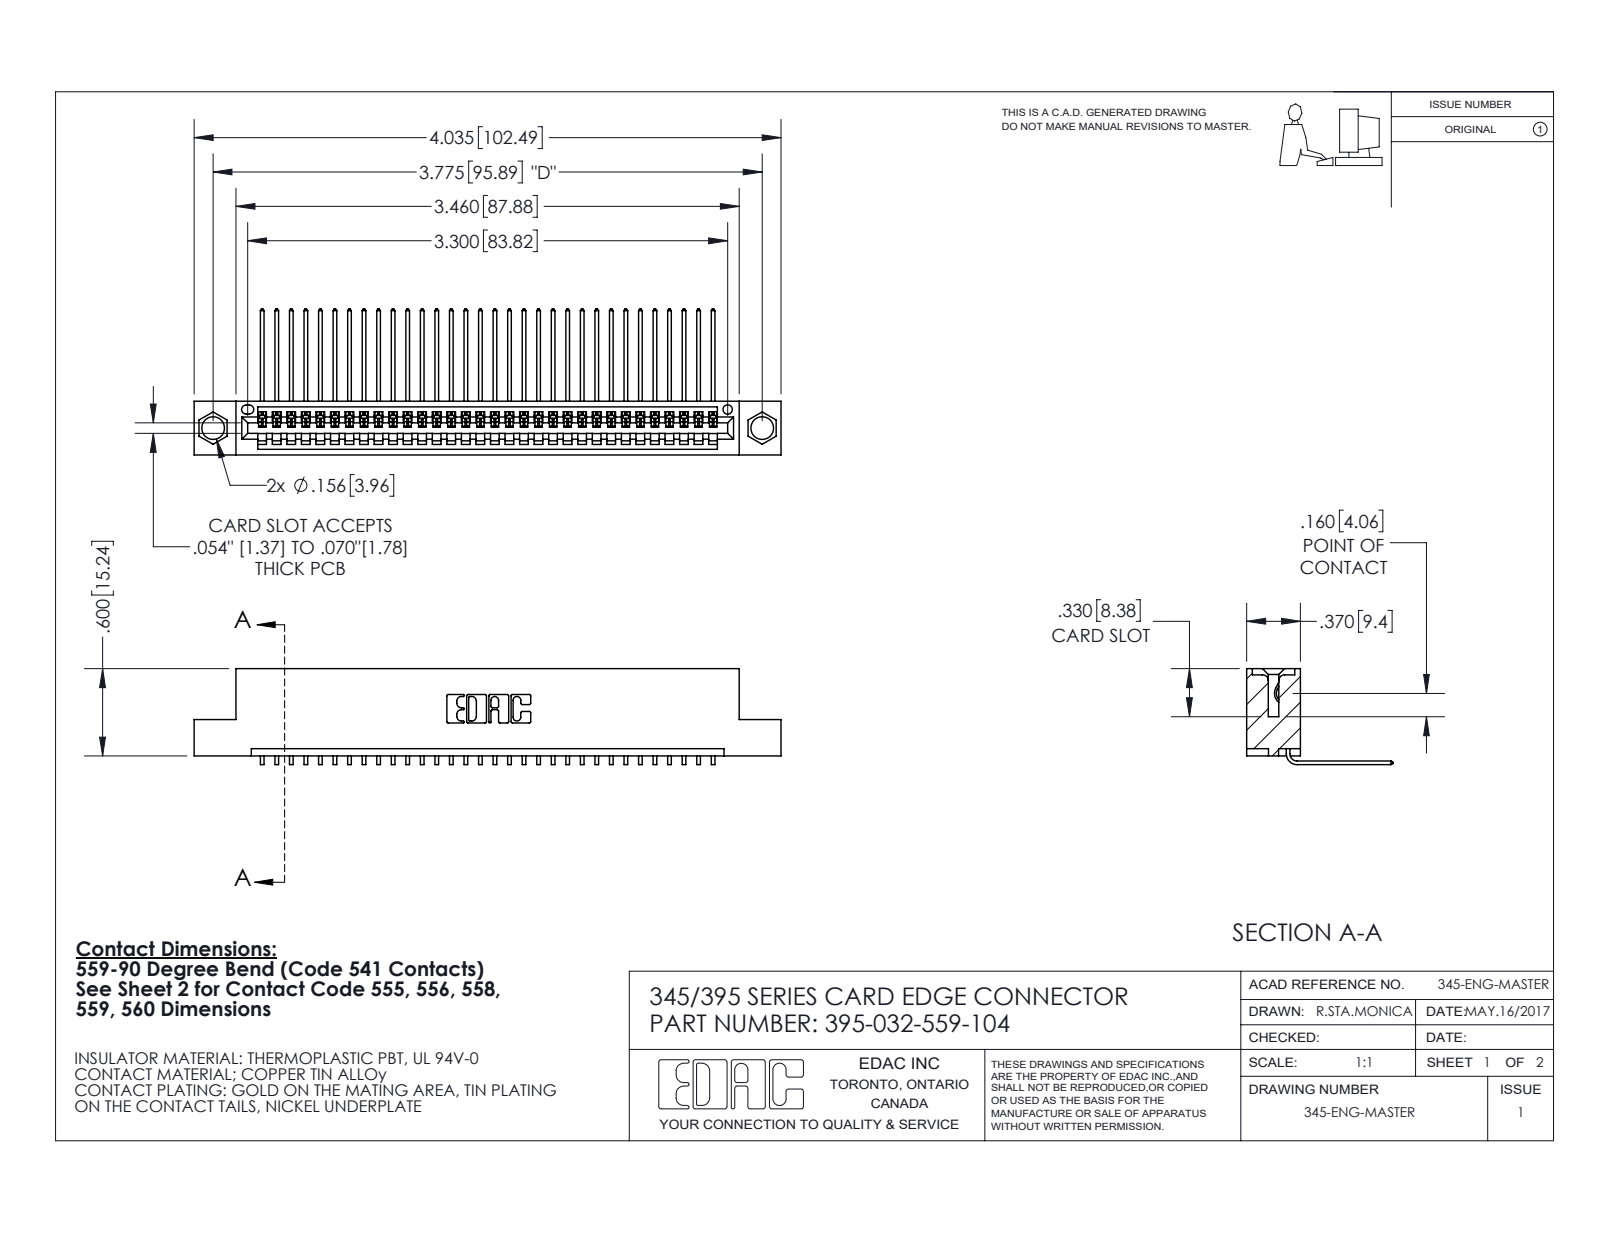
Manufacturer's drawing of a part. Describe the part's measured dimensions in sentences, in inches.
The part is named "345 Part_Flush Mounting Lugs - 0.156 Dia-TI; 345-292-001_558 559 Tail - 1; 395-032-559-104". Its 3-D file was written by "SolidWorks 2020 (CONFIG_CONTROL_DESIGN)". It is 33 solids with 2060 faces: 1438 planar, 622 cylindrical and 0 other. Overall it measures 4.035 by 1.005 by 0.659 inches. Its volume is 0.589 cubic inches and its surface area 20.4 square inches. Round holes: 2 of diameter 0.156, 1 of diameter 0.064. Partial cylindrical surfaces (rounded edges, fillets, slot ends): 64 of radius 0.006, 22 of radius 0.01, 6 of radius 0.007, 6 of radius 0.031, 3 of radius 0.026, 2 of radius 0.031, 2 of radius 0.04, 1 of radius 0.014. The main face-to-face distances are 0.072, 0.298, 0.37, 0.2, 0.098, 0.272, 0.025, 0.225, 0.149, 0.072. The hole center spacings are 0.27, 3.54, 3.775.
